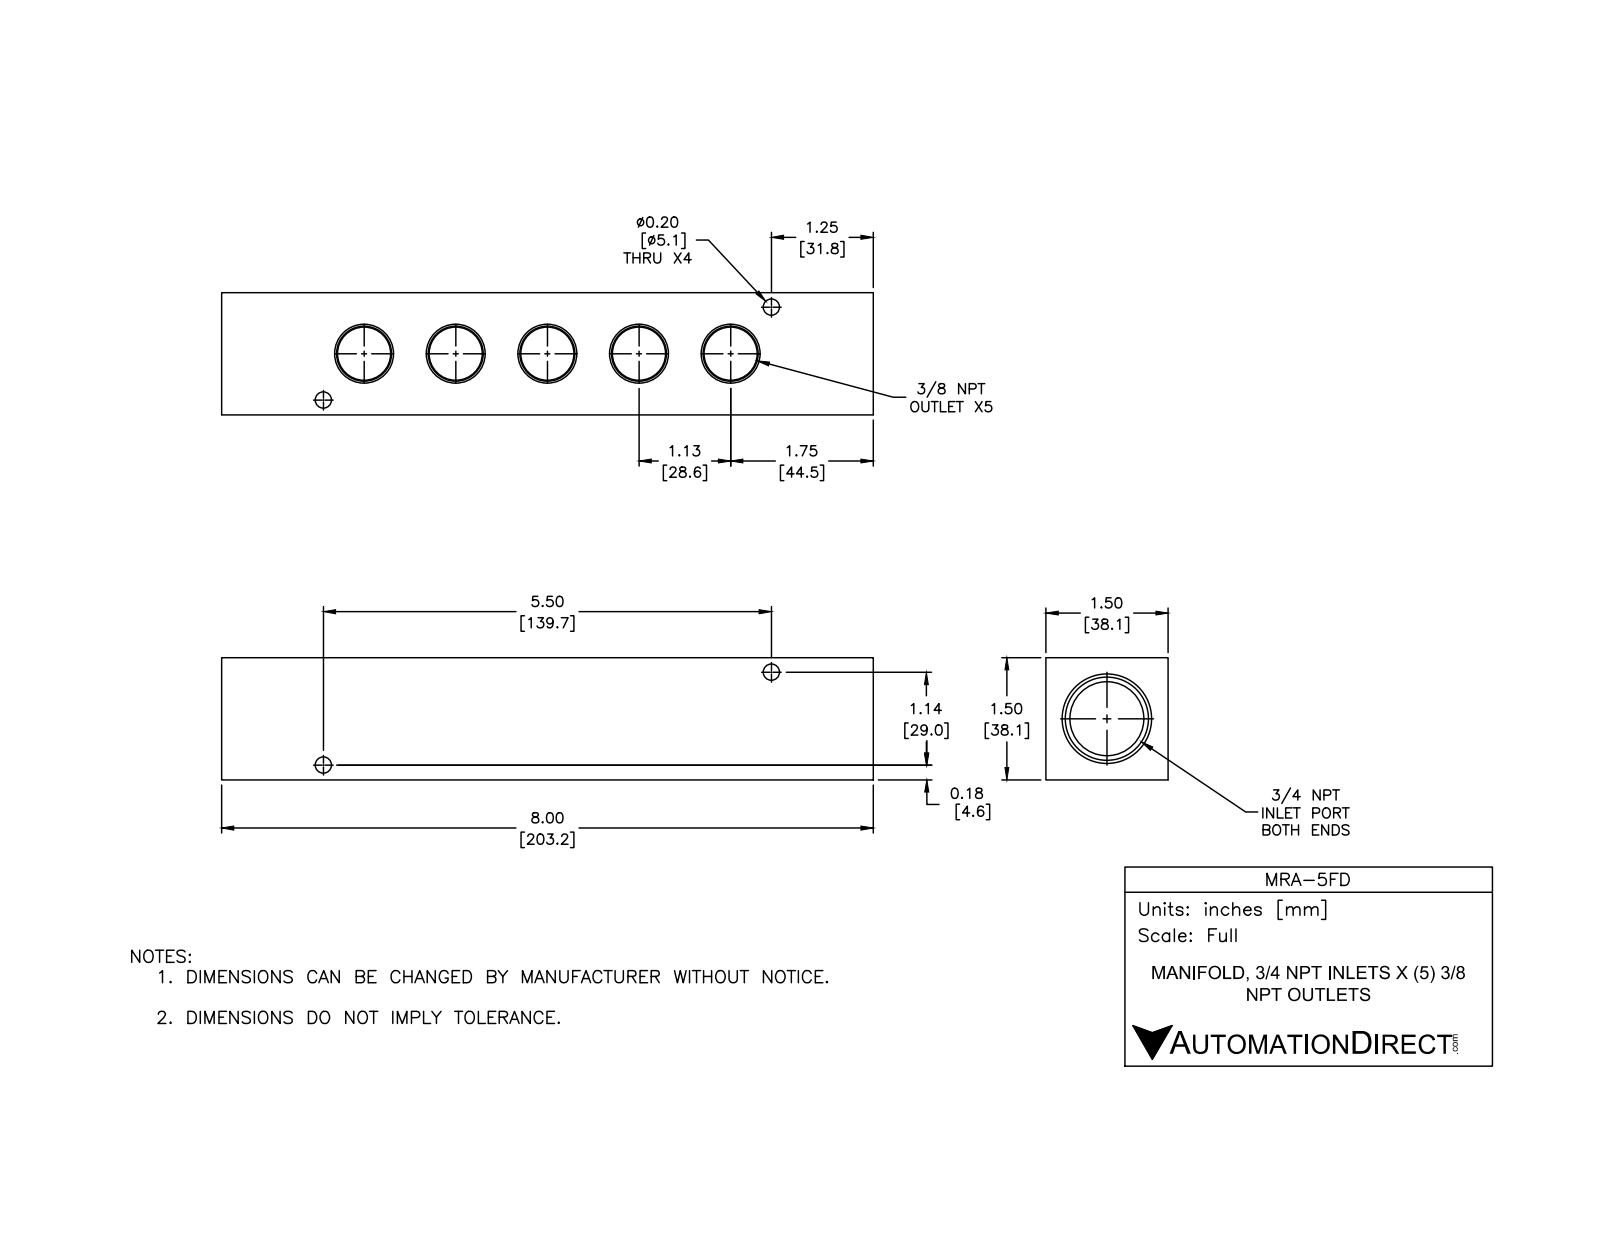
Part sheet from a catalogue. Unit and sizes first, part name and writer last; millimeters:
Units: millimetres
Overall size (bounding box): 203.2 × 38.1 × 38.1
Round holes (diameter × count): ⌀5.1 ×4, ⌀23 ×1
Main face-to-face distances: 38.1, 203.2, 14, 189.2, 175.3, 27.7, 10.4
Hole centre spacings: 142.7
Volume: 194 500 mm³ · Surface area: 50 020 mm²
Bodies: 1 solid, 64 faces (18 planar, 18 cylindrical, 28 other)
Part name (STEP PRODUCT): MRA-5FD
STEP written by: SolidWorks 2015 (CONFIG_CONTROL_DESIGN)
